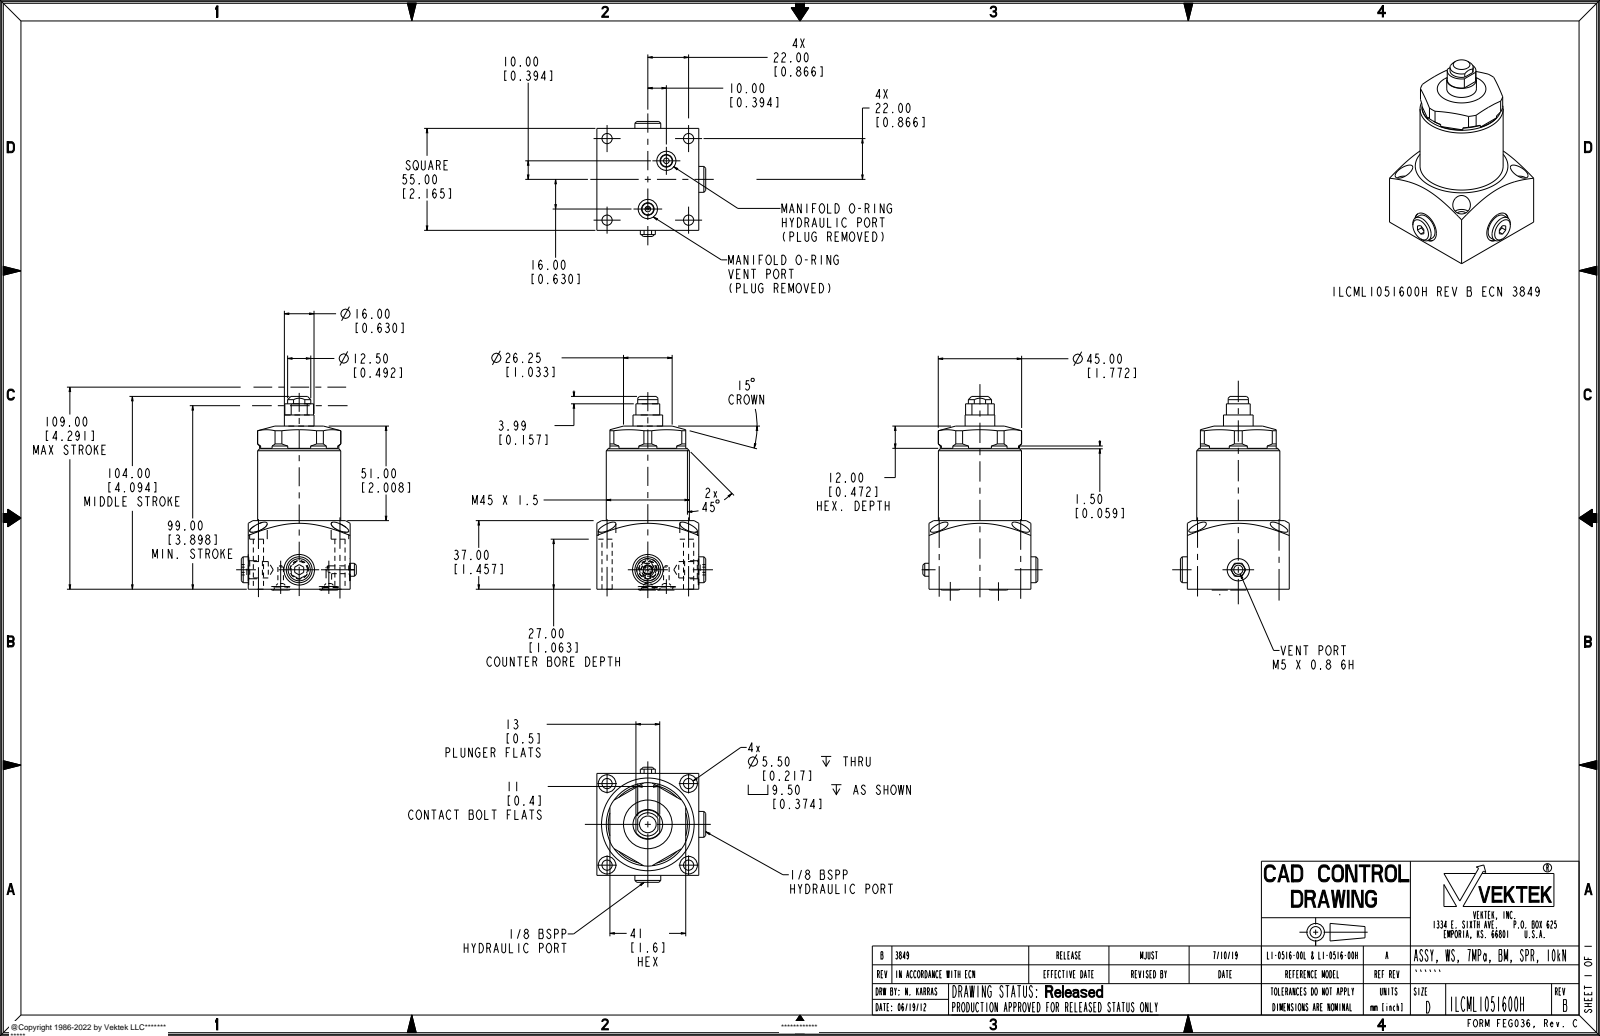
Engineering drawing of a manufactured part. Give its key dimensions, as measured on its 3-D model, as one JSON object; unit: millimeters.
{"part_name": "ILCML1051600H", "step_written_by": "PRO/ENGINEER BY PARAMETRIC TECHNOLOGY CORPORATION, 2017170 (AUTOMOTIVE_DESIGN)", "units": "millimeters", "bodies": {"solids": 1, "faces": 181, "planar": 69, "cylindrical": 64, "other": 48}, "overall_size": [104.45, 62.07, 58.75], "volume_mm3": 184464, "surface_area_mm2": 25956, "round_holes": [[5.5, 4], [9.5, 4], [3, 2], [8.84, 2], [16.51, 2], [4.2, 1], [10, 1], [10.39, 1], [12, 1]], "round_bosses_or_shafts": [[13.97, 2], [9.73, 2], [44.85, 1], [42.75, 1], [16, 1]], "partial_cylinders_radius": [[6.25, 1], [7.75, 1], [22.5, 1]], "face_to_face_distances": [55, 40.92, 37, 54.75, 7.04, 47.96, 88, 51, 27, 10], "hole_center_spacings": [44, 22.8, 34.18, 43.91, 62.23, 16.97, 27.86, 45.25]}
